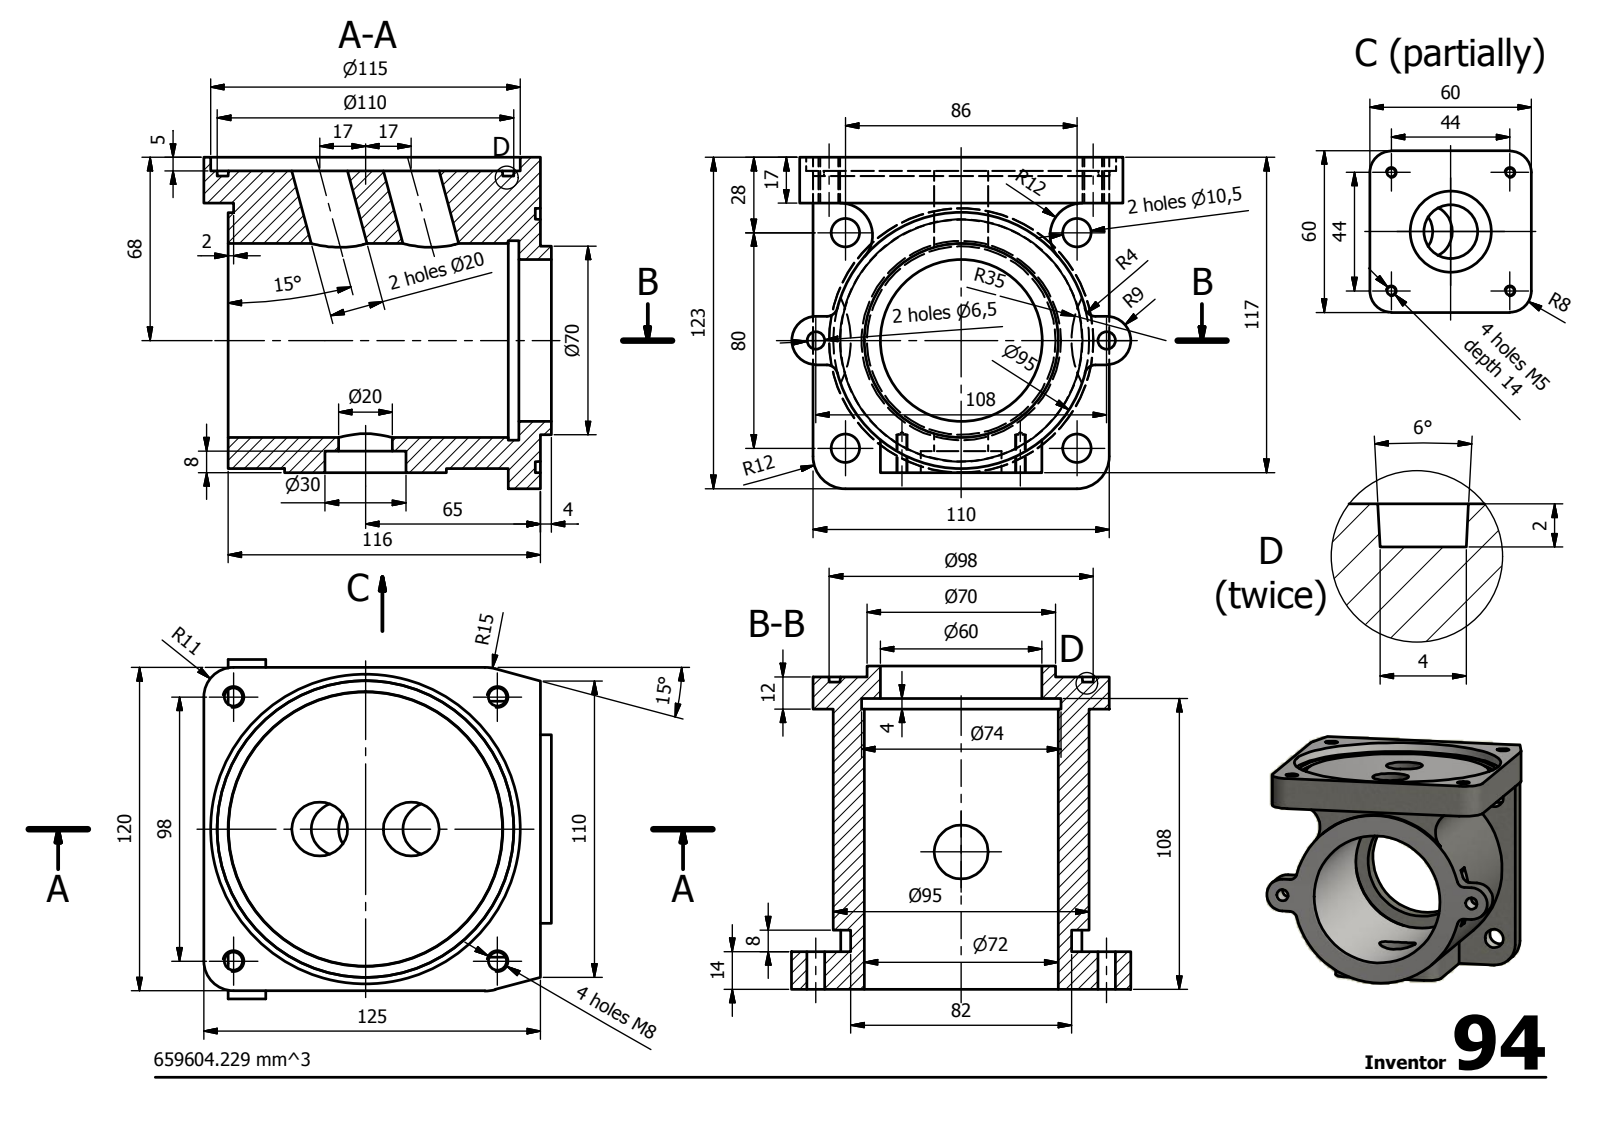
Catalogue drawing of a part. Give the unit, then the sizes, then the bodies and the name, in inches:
Units: inches
Overall size (bounding box): 5.079 × 4.961 × 4.843
Round holes (diameter × count): ⌀0.128 ×4, ⌀0.262 ×4, ⌀0.413 ×4, ⌀0.787 ×3, ⌀0.256 ×2, ⌀1.181 ×1, ⌀2.362 ×1, ⌀2.835 ×1, ⌀2.913 ×1, ⌀4.528 ×1
Round bosses / shafts (diameter × count): ⌀3.74 ×1, ⌀2.756 ×1
Partial cylindrical surfaces — rounded edges, fillets, slot ends (radius × count): R0.157 ×4, R0.315 ×4, R0.472 ×4, R0.354 ×2, R0.433 ×2, R0.591 ×2, R1.378 ×2
Main face-to-face distances: 0.472, 0.197, 4.567, 4.606, 0.669, 4.094, 3.937, 4.409, 0.236, 0.079
Hole centre spacings: 2.991, 1.225, 1.503, 1.633, 1.732, 2.312, 2.728, 3.858
Volume: 40.25 in³ · Surface area: 184 in²
Bodies: 1 solid, 92 faces (40 planar, 44 cylindrical, 8 other)
STEP written by: Autodesk Inventor 2014 (AUTOMOTIVE_DESIGN)
